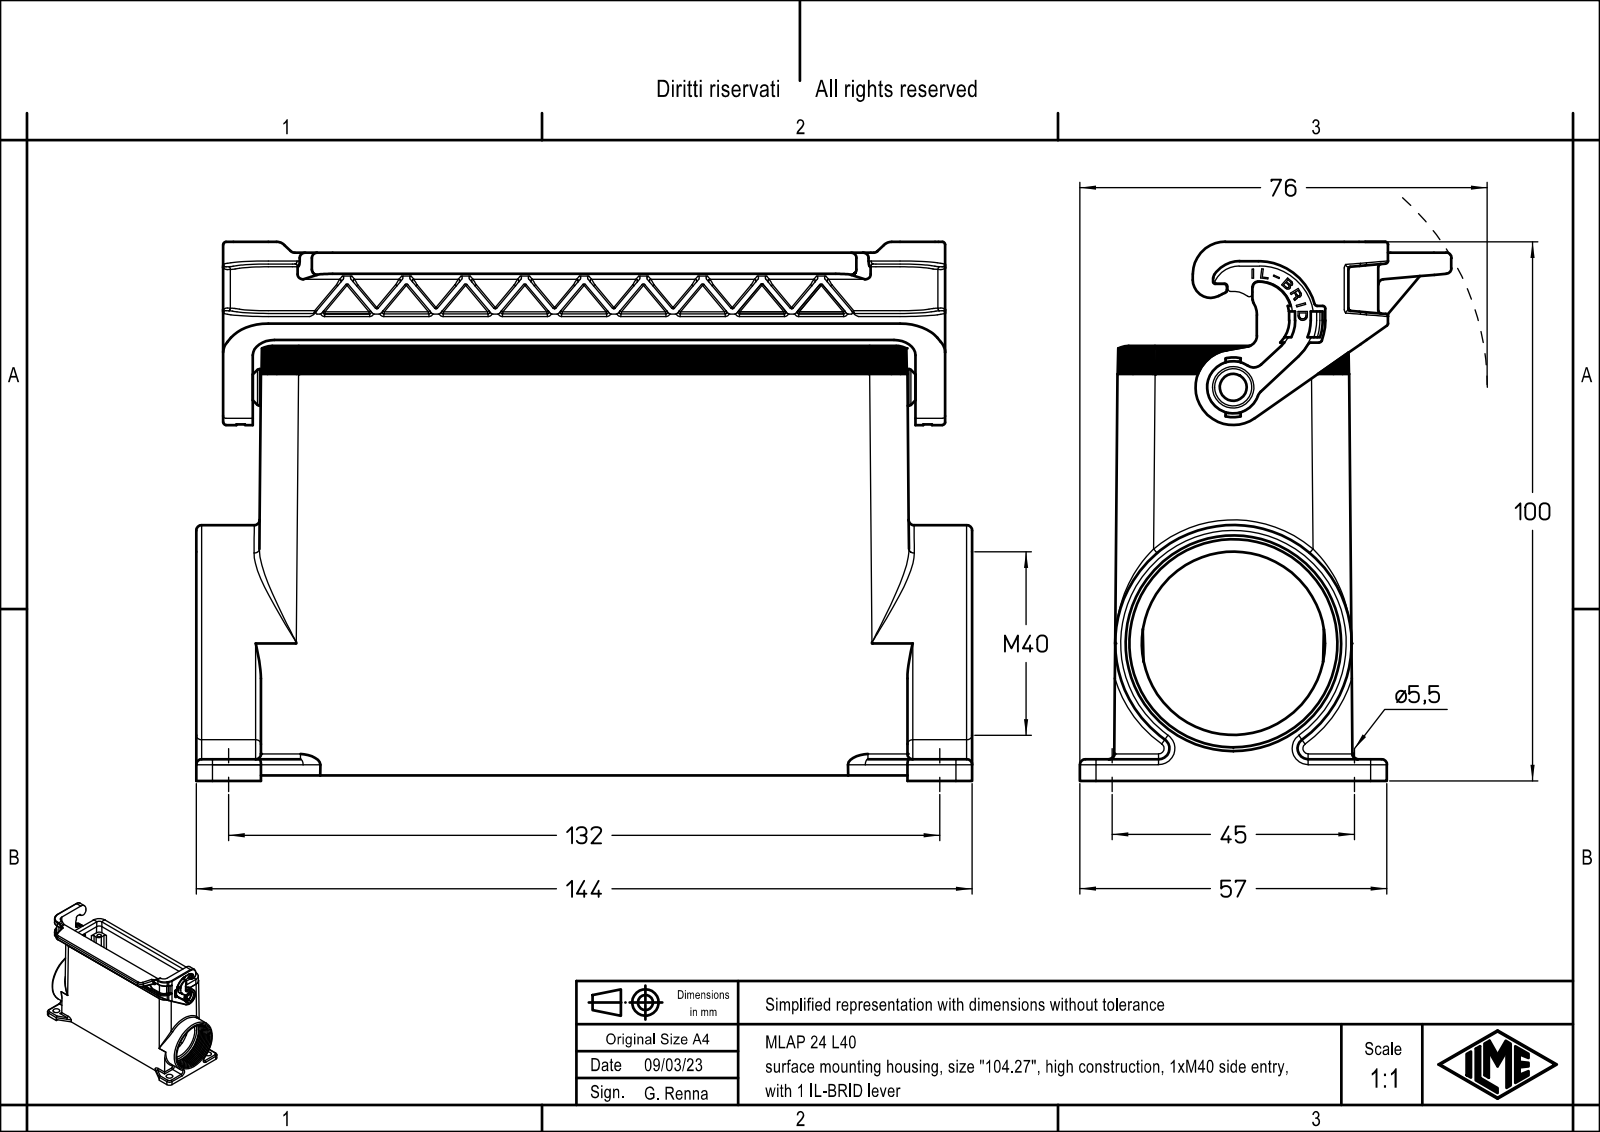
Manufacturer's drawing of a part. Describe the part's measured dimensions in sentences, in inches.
The part is named "MLAP 24 L40". Its 3-D file was written by "Creo Elements/Direct Modeling 20.1B 02-Apr-2019 (C) Parametric Technology GmbH (AUTOMOTIVE_DESIGN)". It is 1 solid with 1083 faces: 655 planar, 294 cylindrical and 134 other. Overall it measures 5.669 by 3.937 by 2.715 inches. Its volume is 9.78 cubic inches and its surface area 127.2 square inches. Round holes: 4 of diameter 0.118, 4 of diameter 0.138, 4 of diameter 0.217, 1 of diameter 0.128, 1 of diameter 0.213, 1 of diameter 0.303, 1 of diameter 1.339, 1 of diameter 1.52. Round bosses or shafts: 1 of diameter 1.727, 1 of diameter 0.272, 1 of diameter 0.268, 1 of diameter 0.205, 1 of diameter 0.126. Partial cylindrical surfaces (rounded edges, fillets, slot ends): 27 of radius 0.004, 16 of radius 0.039, 16 of radius 0.118, 15 of radius 0.008, 11 of radius 0.02, 11 of radius 0.079, 10 of radius 0.276, 9 of radius 0.059. The main face-to-face distances are 0.118, 0.217, 0.157, 3.819, 3.701, 4.843, 0.039, 0.276, 1.531, 0.197. The hole center spacings are 0.655, 1.521, 4.659, 4.857, 1.063, 1.772, 4.094, 4.23.
